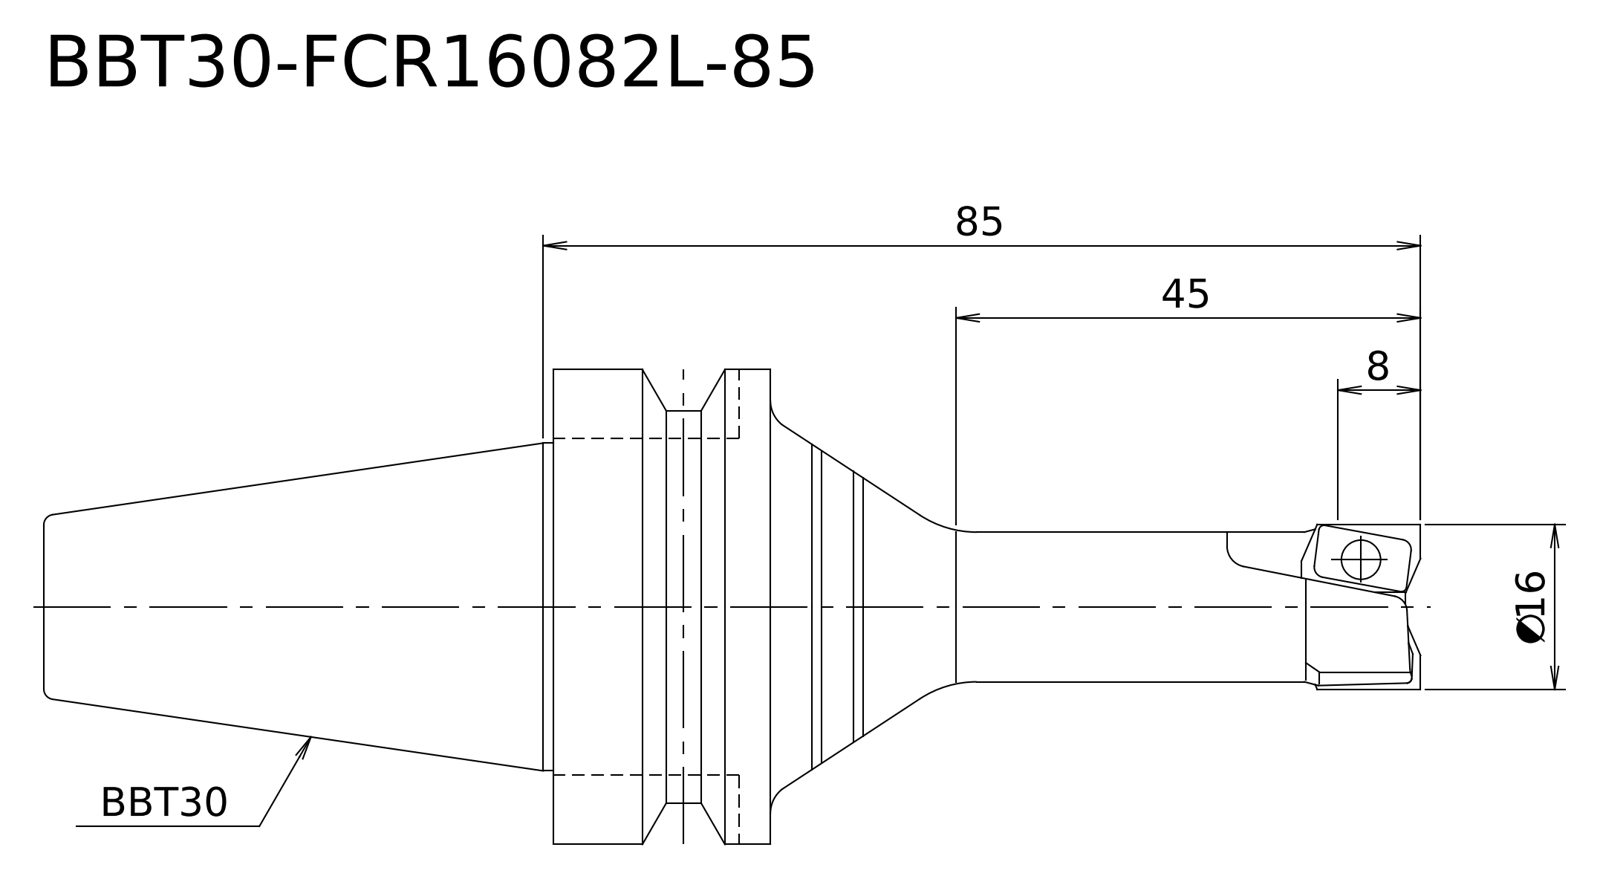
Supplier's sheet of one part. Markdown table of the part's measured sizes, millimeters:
| quantity | value |
| --- | --- |
| STEP written by | Kubotek KeyCreator V8.5.1 (14335) (CONFIG_CONTROL_DESIGN) |
| units | millimeters |
| bodies | 1 solid, 17 faces (4 planar, 6 cylindrical, 7 other) |
| overall size | 133.4 × 46 × 46 |
| volume | 73 961 mm³ |
| surface area | 13 057 mm² |
| round bosses / shafts (diameter × count) | 46 × 1, 38 × 1, 31.75 × 1, 16 × 1, 14.5 × 1 |
| main face-to-face distances | 21, 70.4, 49.4, 63, 84, 133.4 |
